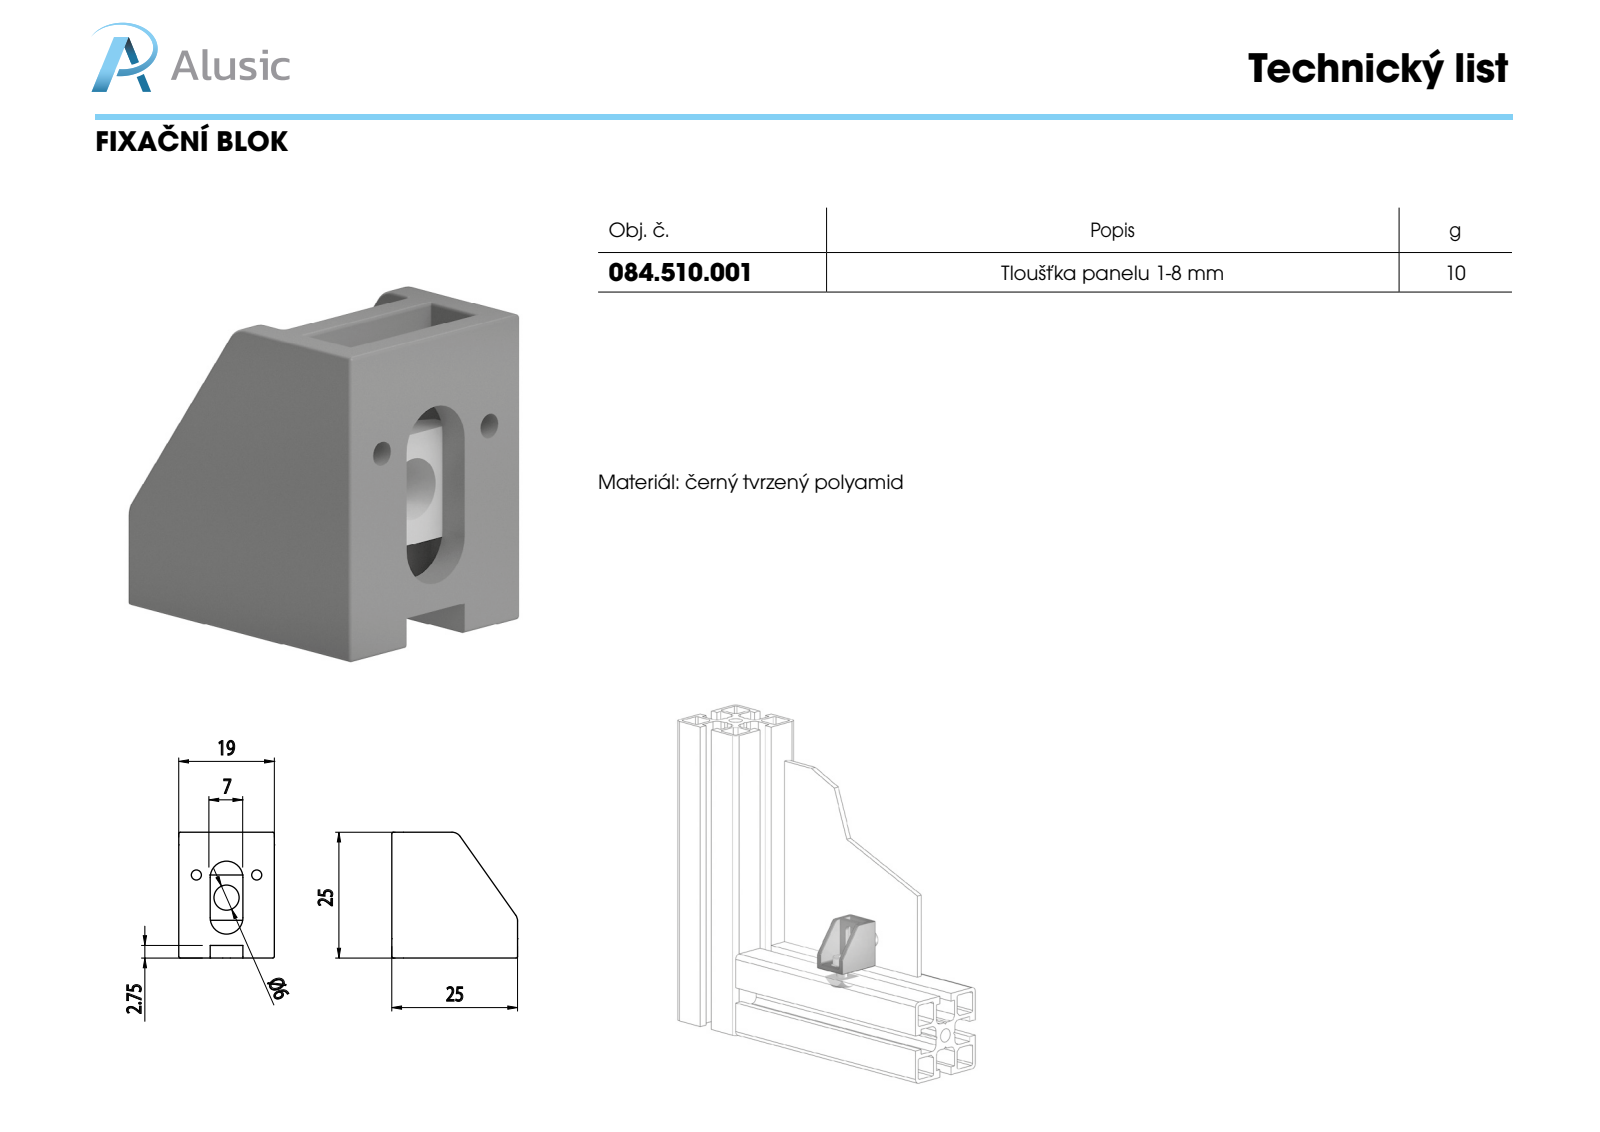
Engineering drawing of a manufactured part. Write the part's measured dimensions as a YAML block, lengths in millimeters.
part_name: "084.510.001"
step_written_by: "SolidWorks 2011 (CONFIG_CONTROL_DESIGN)"
units: millimeters
bodies: {solids: 2, faces: 103, planar: 33, cylindrical: 48, other: 22}
overall_size: [25, 25, 19]
volume: 4394
surface_area: 4140
round_holes:
  - {diameter: 2, count: 2}
  - {diameter: 5, count: 1}
partial_cylinders:
  - {radius: 0.3, count: 26}
  - {radius: 2.5, count: 4}
  - {radius: 1, count: 2}
  - {radius: 2, count: 2}
  - {radius: 3.25, count: 2}
face_to_face_distances: [2.5, 16.5, 19, 14, 7.5, 5, 6.25, 12.75, 3.75, 10.25]
hole_center_spacings: [7.5, 12]
